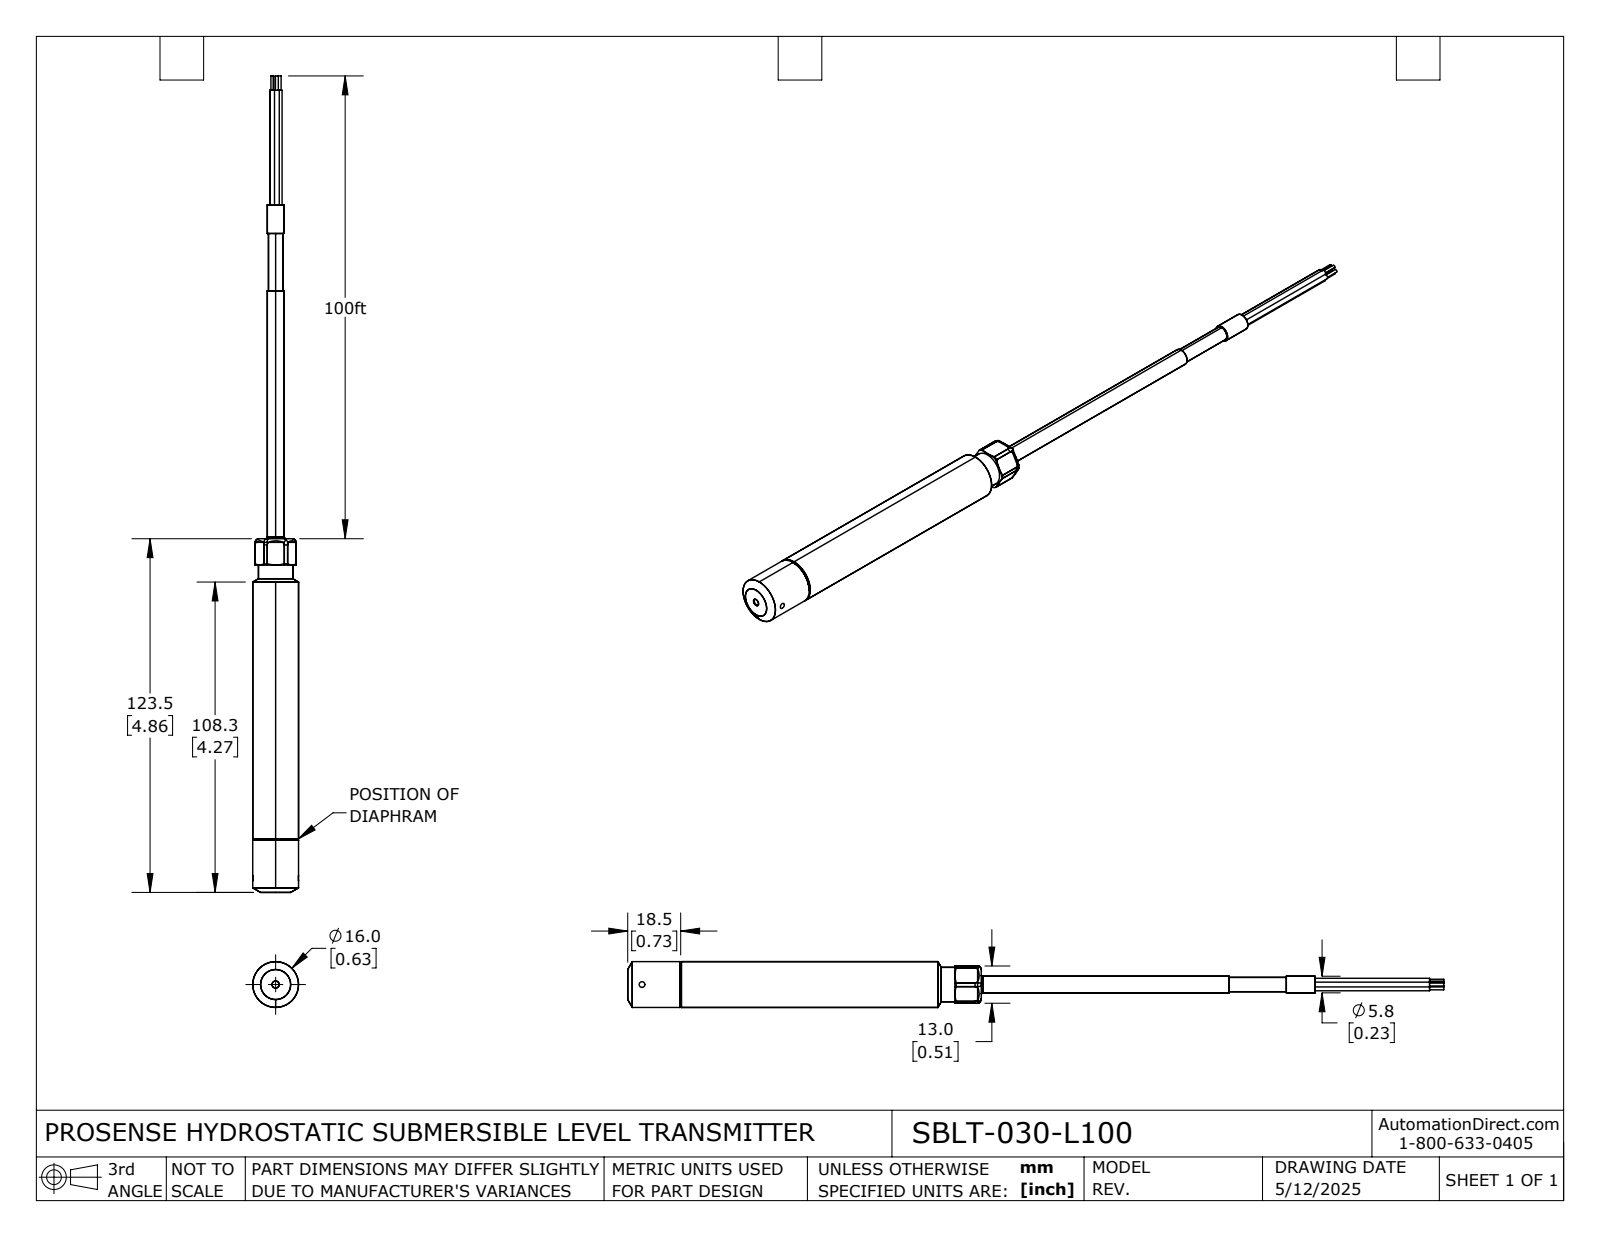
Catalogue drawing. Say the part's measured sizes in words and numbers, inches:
The part is named "SBLT-030-L100". Its 3-D file was written by "SolidWorks 2024 (AUTOMOTIVE_DESIGN)". It is 11 solids with 201 faces: 52 planar, 88 cylindrical and 61 other. Overall it measures 11.221 by 0.63 by 0.63 inches. Its volume is 3.198 cubic inches and its surface area 29.94 square inches. Round holes: 1 of diameter 0.079, 1 of diameter 0.098, 1 of diameter 0.374, 1 of diameter 0.516, 1 of diameter 0.551. Round bosses or shafts: 5 of diameter 0.066, 5 of diameter 0.039, 1 of diameter 0.63, 1 of diameter 0.629, 1 of diameter 0.472, 1 of diameter 0.472, 1 of diameter 0.244, 1 of diameter 0.228. Partial cylindrical surfaces (rounded edges, fillets, slot ends): 6 of radius 0.05, 1 of radius 0.281. The main face-to-face distances are 0.512, 4.861, 4.33, 0.531, 4.589, 8.918, 9.45, 3.77, 0.197, 8.721.
